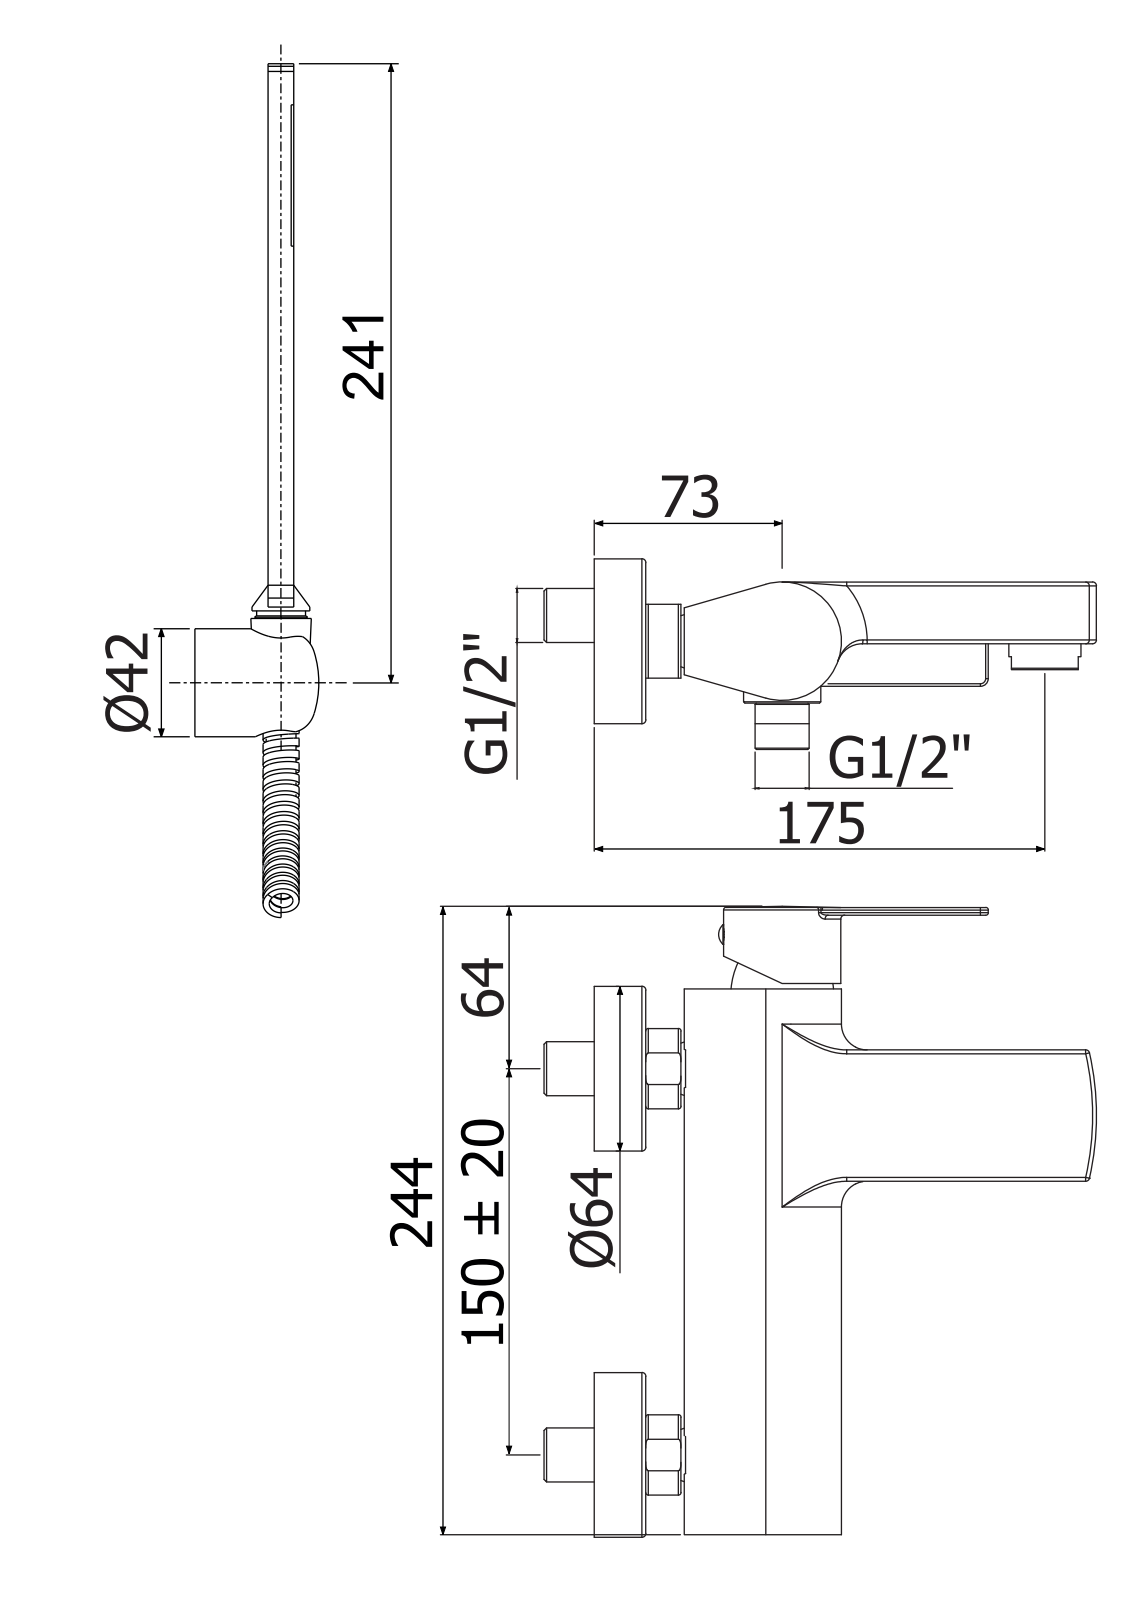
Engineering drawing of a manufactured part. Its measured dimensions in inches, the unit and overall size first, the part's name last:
Units: inches
Overall size (bounding box): 17.165 × 14.22 × 7.697
Round holes (diameter × count): ⌀0.965 ×3, ⌀0.984 ×3, ⌀0.197 ×2, ⌀0.315 ×2, ⌀0.413 ×2, ⌀0.65 ×2, ⌀0.85 ×2, ⌀2.453 ×2, ⌀0.118 ×1, ⌀0.138 ×1, ⌀0.165 ×1, ⌀0.276 ×1
Round bosses / shafts (diameter × count): ⌀1.063 ×3, ⌀0.945 ×3, ⌀2.5 ×2, ⌀0.748 ×2, ⌀1.791 ×1, ⌀1.654 ×1, ⌀1.457 ×1, ⌀1.181 ×1
Partial cylindrical surfaces — rounded edges, fillets, slot ends (radius × count): R0.059 ×10, R0.039 ×6, R0.138 ×3, R0.02 ×2, R0.118 ×2, R0.614 ×2, R0.374 ×1, R0.394 ×1
Main face-to-face distances: 0.138, 0.118, 0.394, 1.122, 0.512, 0.787, 0.276, 1.87, 1.24, 0.335
Hole centre spacings: 0.236, 0.709, 2.051, 5.906, 6.064, 6.806, 7.395, 7.957
Volume: 26.54 in³ · Surface area: 375 in²
Bodies: 3 solids, 672 faces (257 planar, 206 cylindrical, 209 other)
Part name (STEP PRODUCT): TA026CR
STEP written by: CREO PARAMETRIC BY PTC INC, 2020044 (CONFIG_CONTROL_DESIGN)
